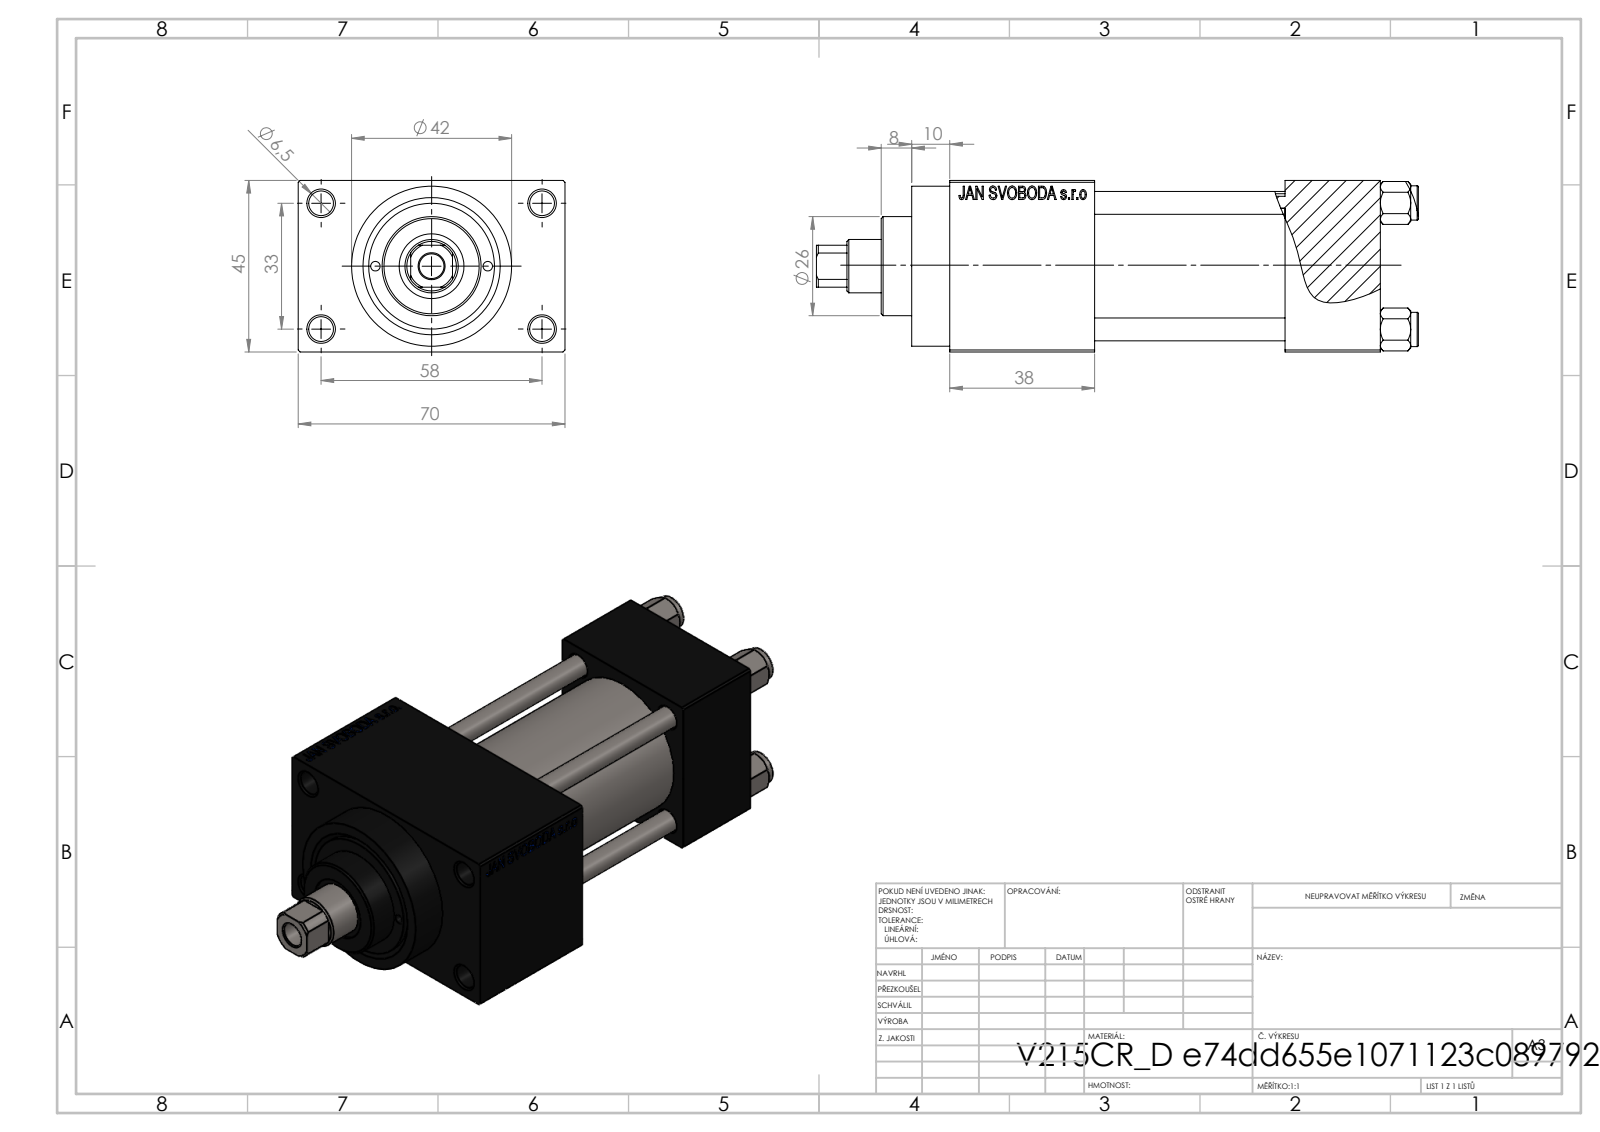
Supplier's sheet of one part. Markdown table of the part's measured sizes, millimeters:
| quantity | value |
| --- | --- |
| part name | V215_VC_A; V215CR_VCP_D; V215CR_D_Body; V215CR_D_TYCINKA (+1 more) |
| STEP written by | SolidWorks 2019 (CONFIG_CONTROL_DESIGN) |
| units | millimeters |
| bodies | 11 solids, 1110 faces (498 planar, 92 cylindrical, 520 other) |
| overall size | 158 × 70 × 45 |
| volume | 230 158 mm³ |
| surface area | 75 379 mm² |
| round holes (diameter × count) | 6.5 × 5, 6 × 4, 2.5 × 2, 7 × 2, 13.16 × 2, 20 × 2, 14 × 1, 17 × 1, 24 × 1, 32 × 1, 33 × 1 |
| round bosses / shafts (diameter × count) | 9 × 4, 42 × 1, 38 × 1, 26 × 1 |
| partial cylindrical surfaces (radius × count) | 6.5 × 1 |
| main face-to-face distances | 45, 25, 50, 12.5, 75, 57.5, 88, 38, 113, 70 |
| hole center spacings | 12.4, 16.7, 21.8, 23.48, 33.2, 33.37, 35.35, 35.47 |
